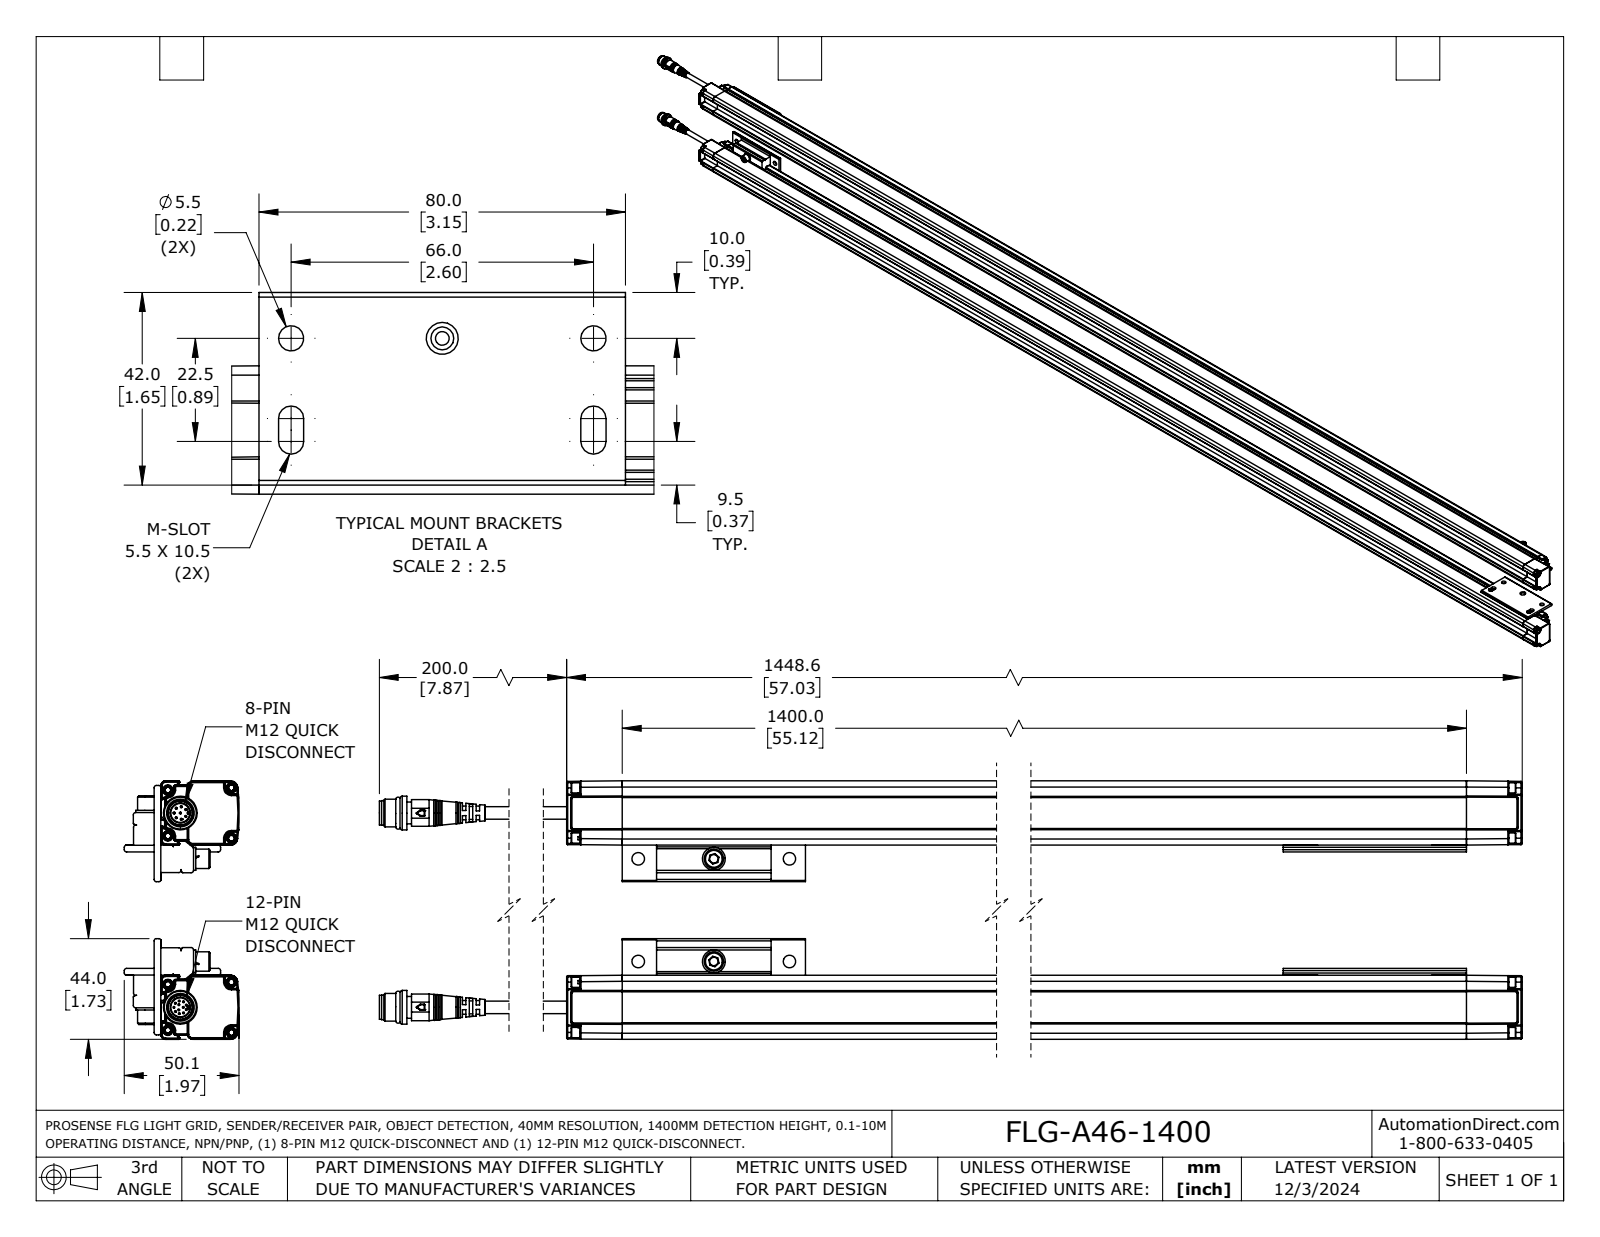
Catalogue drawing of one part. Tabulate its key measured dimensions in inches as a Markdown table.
| quantity | value |
| --- | --- |
| part name | FLG-A46-1400 |
| STEP written by | SolidWorks 2023 (AUTOMOTIVE_DESIGN) |
| units | inches |
| bodies | 5 solids, 869 faces (435 planar, 238 cylindrical, 196 other) |
| overall size | 60.652 × 1.972 × 1.732 |
| volume | 70.77 in³ |
| surface area | 437.5 in² |
| round holes (diameter × count) | 0.016 × 16, 0.217 × 4, 0.098 × 2, 0.197 × 2, 0.327 × 1 |
| round bosses / shafts (diameter × count) | 0.031 × 8, 0.177 × 4, 0.118 × 4, 0.394 × 2, 0.335 × 2, 0.217 × 2, 0.146 × 2, 0.059 × 2 |
| partial cylindrical surfaces (radius × count) | 0.02 × 76, 0.039 × 20, 0.01 × 10, 0.108 × 8, 0.008 × 6, 0.012 × 6, 0.1 × 4, 0.049 × 2 |
| main face-to-face distances | 1.102, 0.071, 0.817, 0.285, 0.97, 1.041, 0.215, 1.031, 0.746, 0.531 |
| hole center spacings | 0.108, 0.163, 1.299, 0.215, 0.089, 0.09, 0.09, 0.118 |
